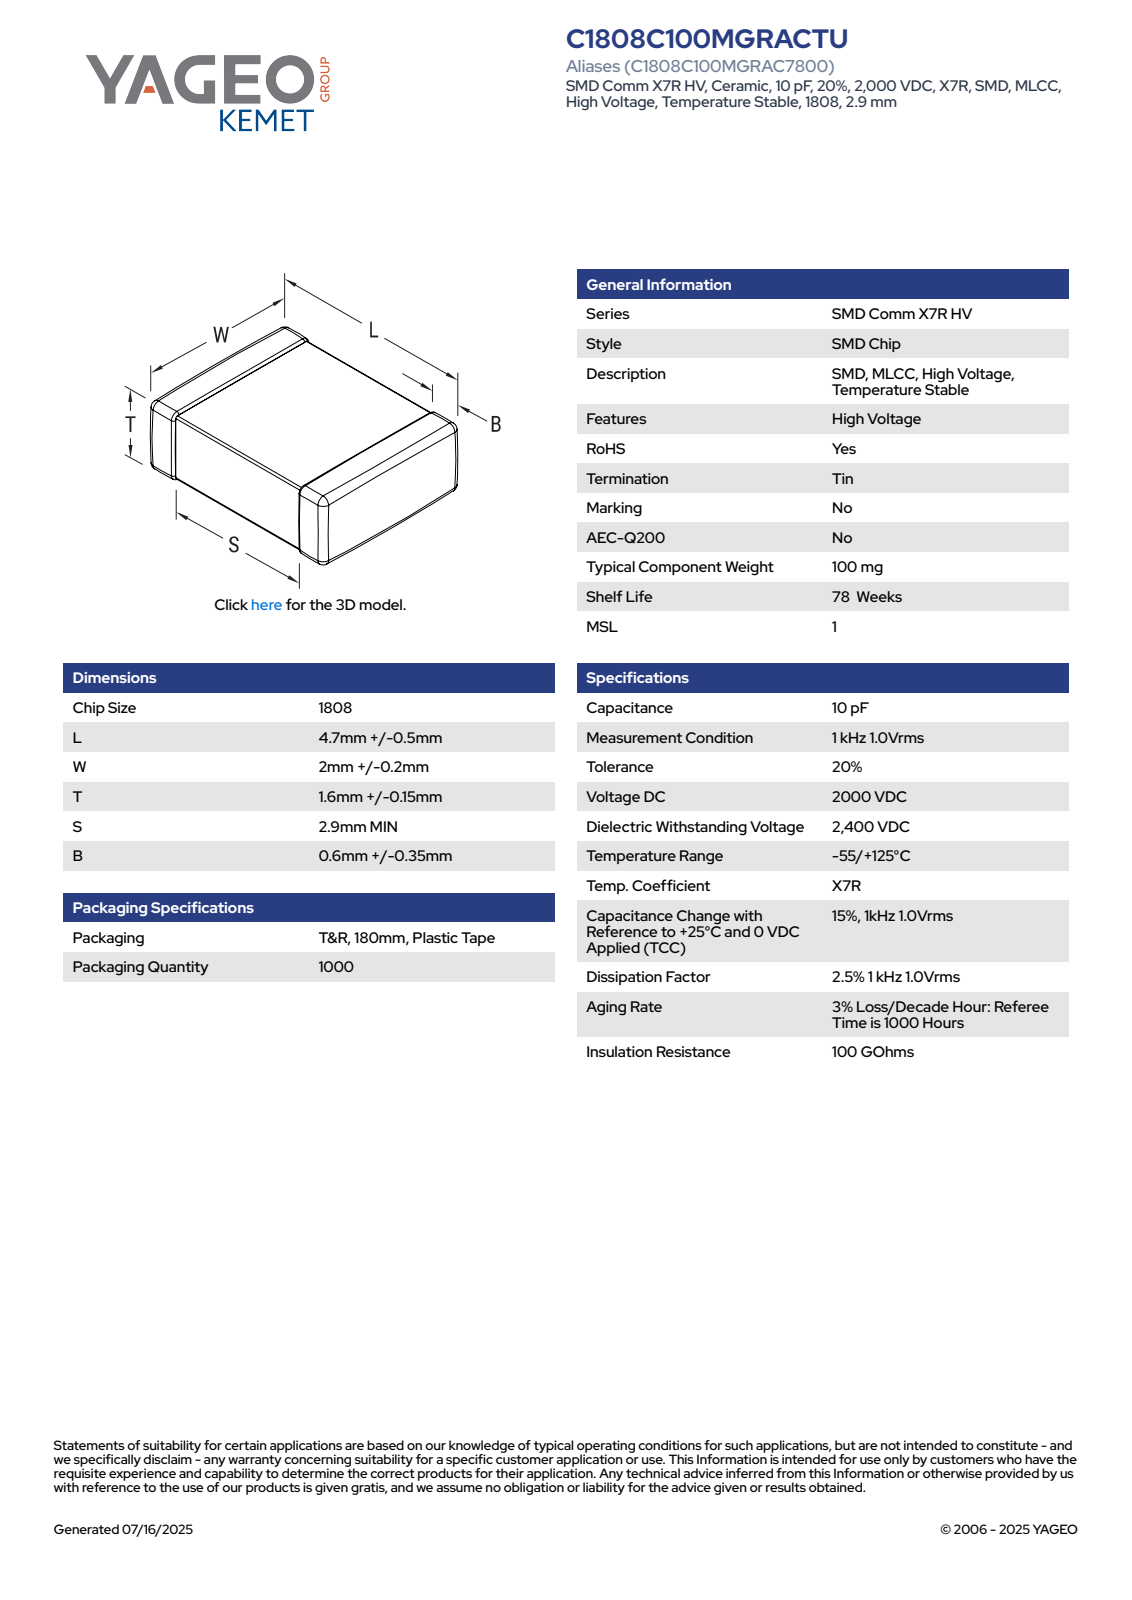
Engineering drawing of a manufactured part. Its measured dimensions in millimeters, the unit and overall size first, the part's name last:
Units: millimetres
Overall size (bounding box): 5.2 × 2.2 × 1.75
Main face-to-face distances: 1.7, 1.65, 2.15, 2.1, 1.75, 5.2, 2.2, 1.71, 1.66, 0.33
Volume: 19 mm³ · Surface area: 48 mm²
Bodies: 4 solids, 125 faces (71 planar, 38 cylindrical, 16 other)
Part name (STEP PRODUCT): CCS_CCSTD_1808_L5.2W2.2T1.75B0.6
STEP written by: SolidWorks 2021 (AUTOMOTIVE_DESIGN)
